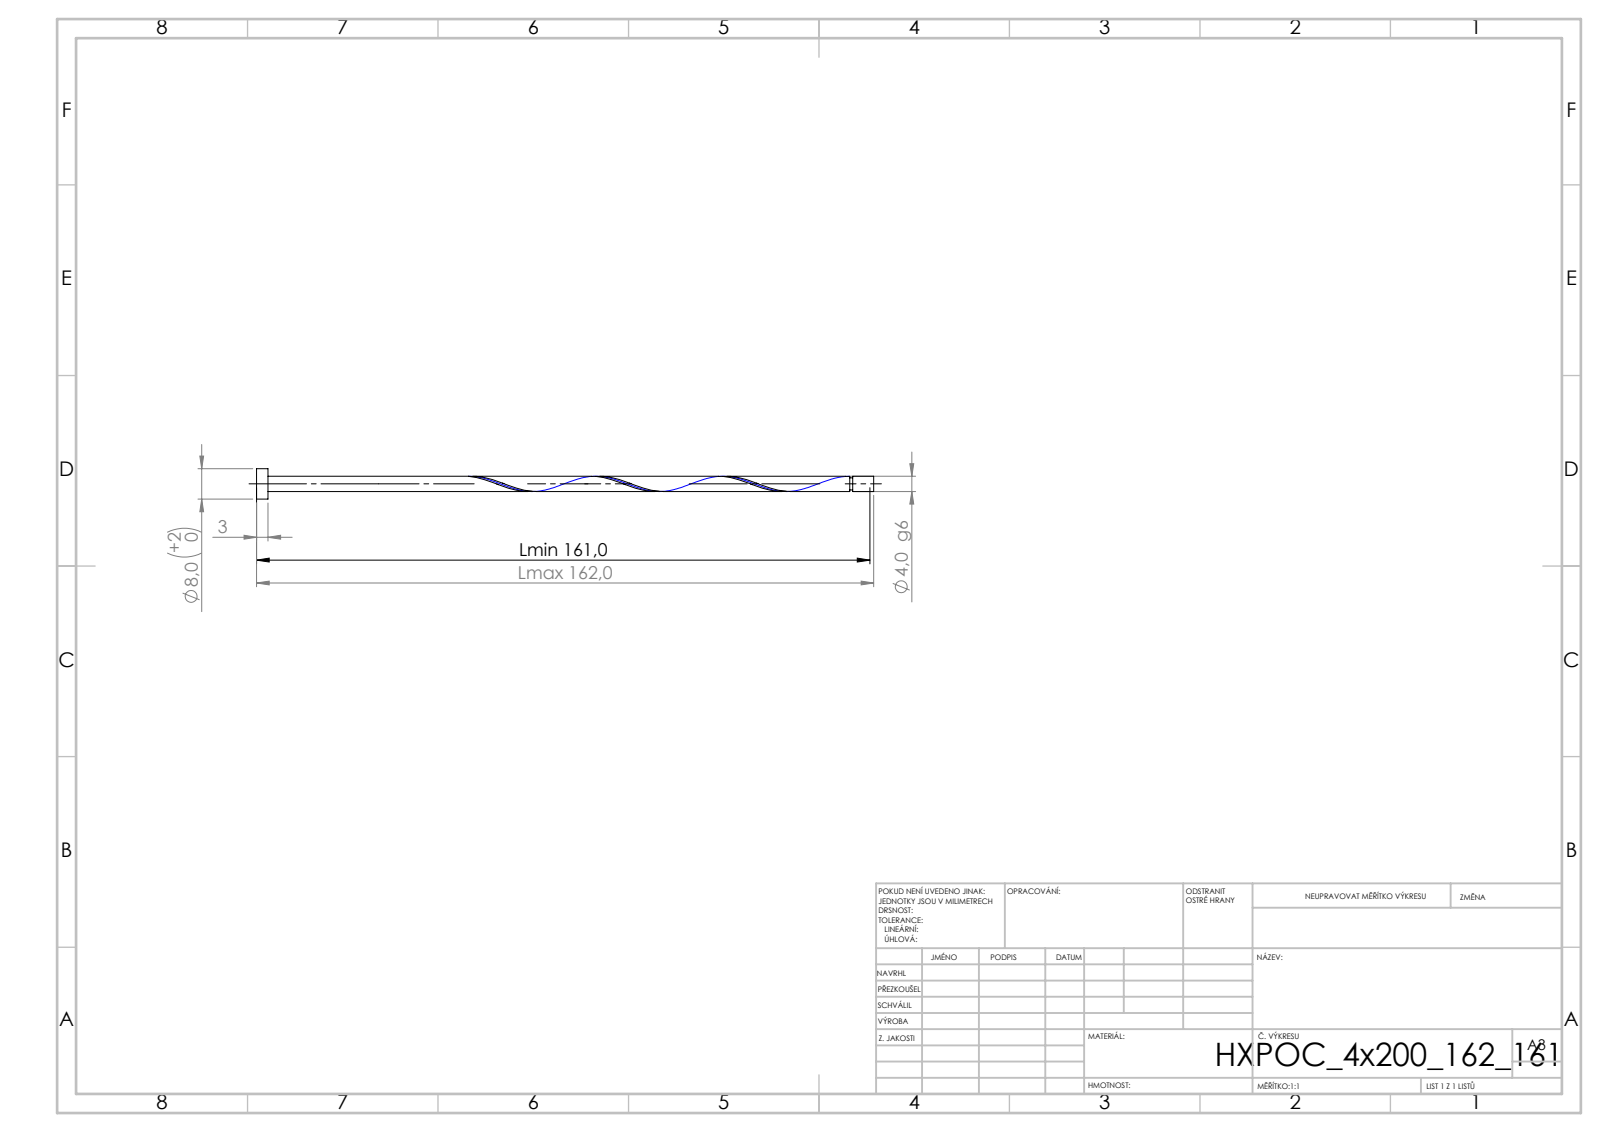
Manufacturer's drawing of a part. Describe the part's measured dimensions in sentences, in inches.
Its 3-D file was written by "SolidWorks 2019 (CONFIG_CONTROL_DESIGN)". It is 1 solid with 21 faces: 6 planar, 14 cylindrical and 1 other. Overall it measures 6.378 by 0.315 by 0.315 inches. Its volume is 0.129 cubic inches and its surface area 3.444 square inches. Round bosses or shafts: 1 of diameter 0.315, 1 of diameter 0.157, 1 of diameter 0.126. The main face-to-face distances are 0.118, 6.378, 6.26, 6.161, 6.043, 0.217, 6.13, 6.011, 0.031, 0.248.
